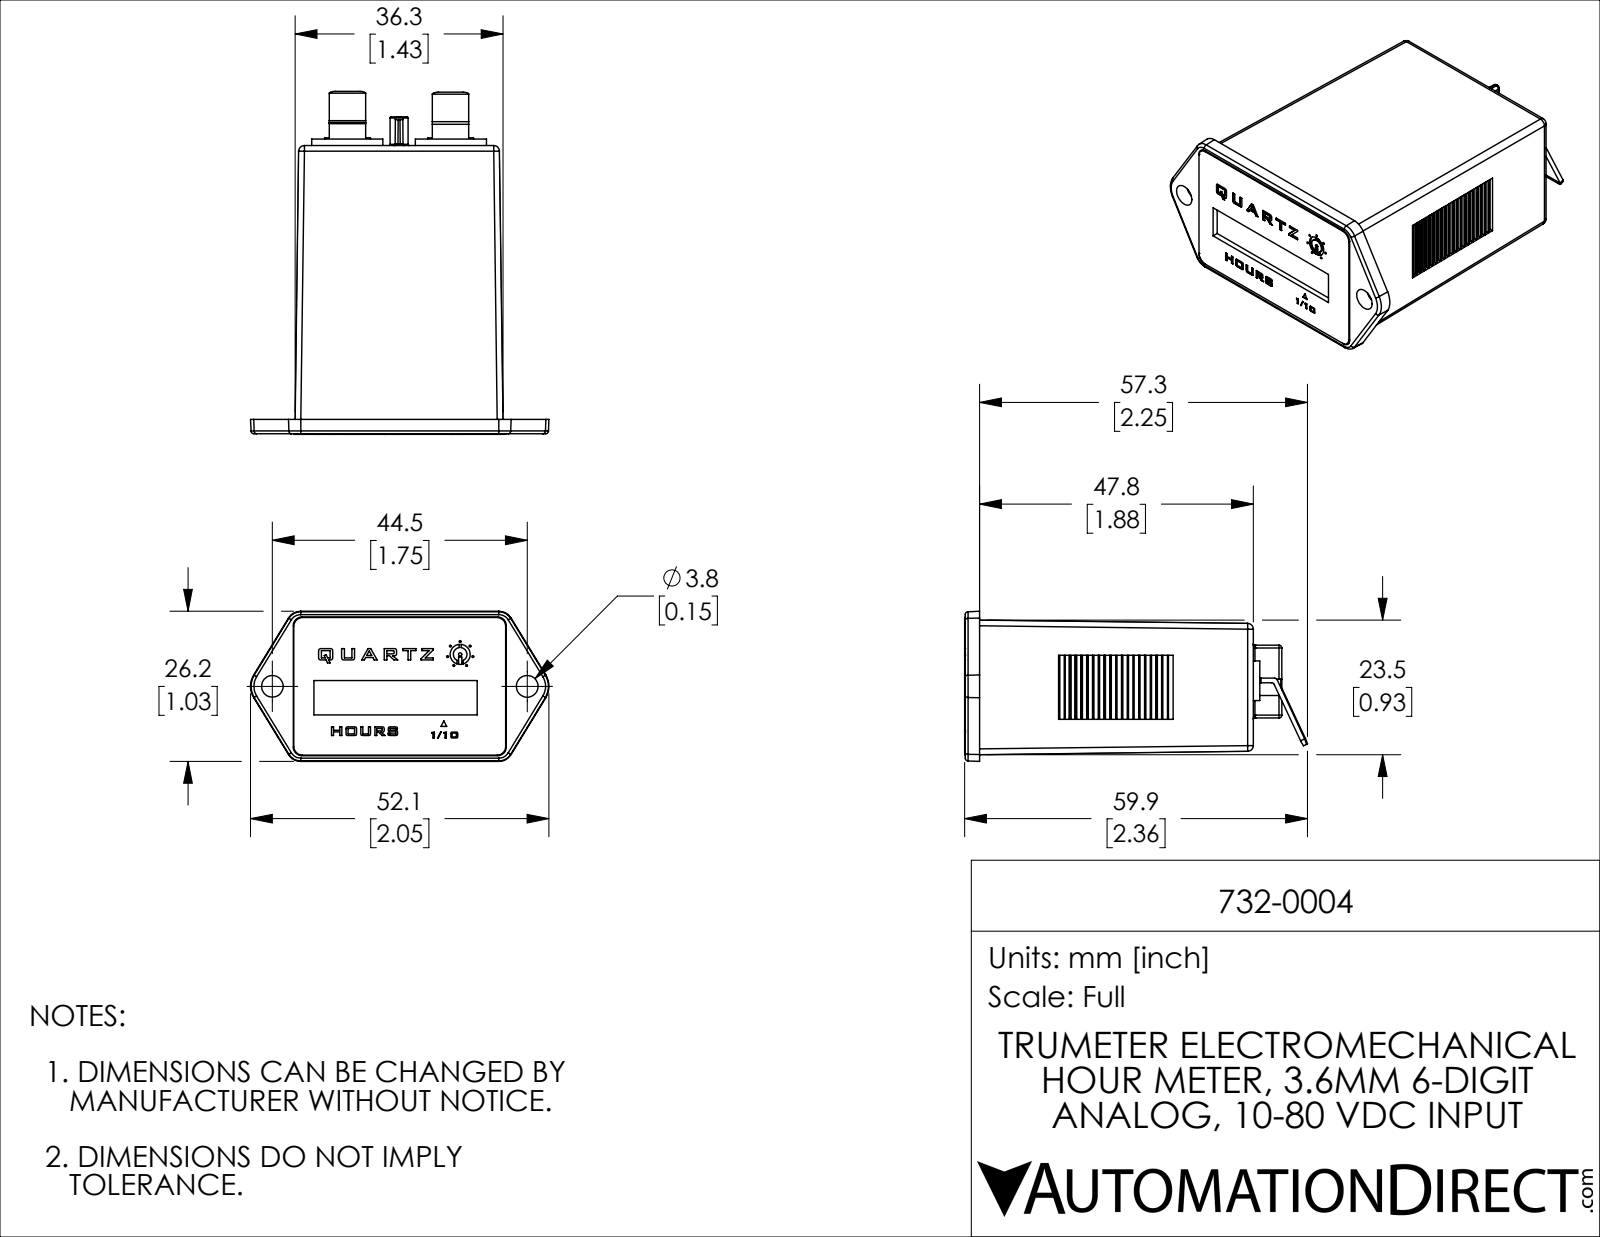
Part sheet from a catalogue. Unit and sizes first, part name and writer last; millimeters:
Units: millimetres
Overall size (bounding box): 59.86 × 52.1 × 26.2
Round holes (diameter × count): ⌀0.34 ×7, ⌀1.5 ×4, ⌀0.56 ×1, ⌀3.51 ×1, ⌀3.77 ×1, ⌀3.8 ×1
Round bosses / shafts (diameter × count): ⌀2.38 ×1
Partial cylindrical surfaces — rounded edges, fillets, slot ends (radius × count): R0.5 ×32, R1 ×17, R0.3 ×15, R1.5 ×10, R0.35 ×4, R1.91 ×2, R1.57 ×1
Main face-to-face distances: 1, 47.55, 48.55, 1.85, 50.4, 49.4, 1.6, 0.8, 2.6, 45.95
Hole centre spacings: 2.24, 3.44, 1.9, 4.34, 2.25, 4.42, 1.89, 3.67
Volume: 10 688 mm³ · Surface area: 17 145 mm²
Bodies: 5 solids, 718 faces (536 planar, 126 cylindrical, 56 other)
Part name (STEP PRODUCT): 732-0004
STEP written by: SolidWorks 2021 (CONFIG_CONTROL_DESIGN)
